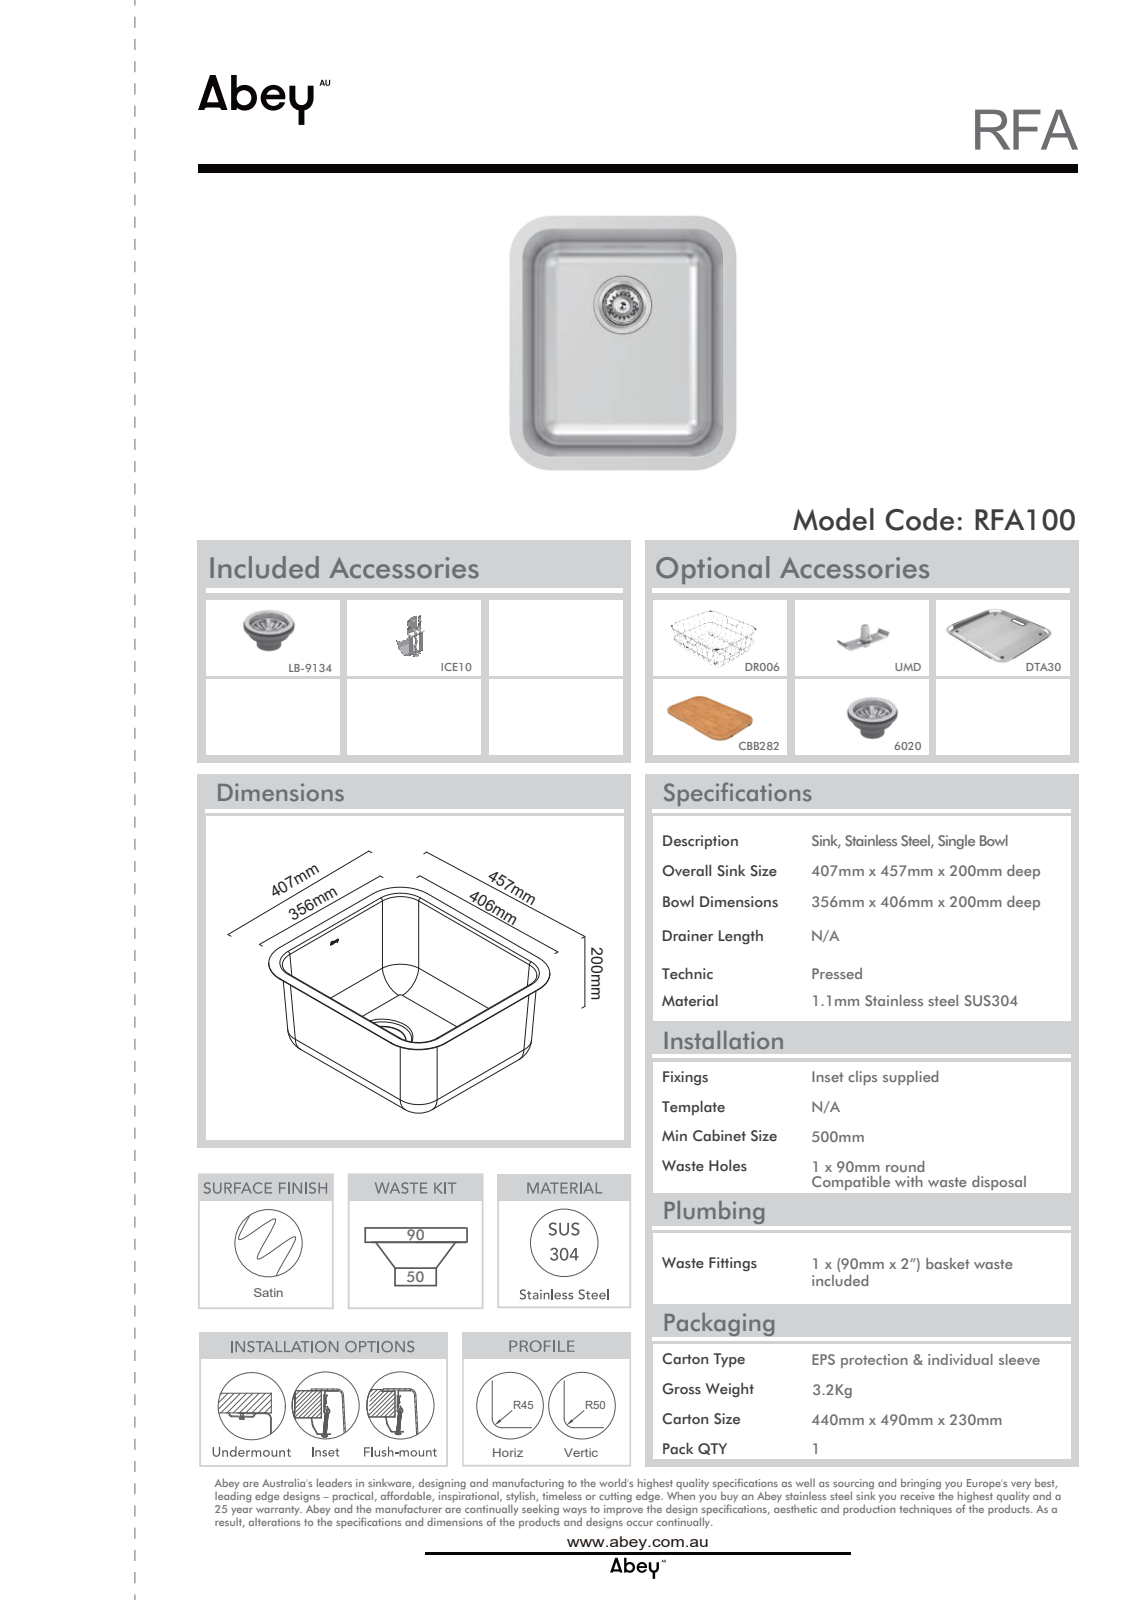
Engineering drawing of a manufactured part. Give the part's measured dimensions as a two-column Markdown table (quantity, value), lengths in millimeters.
| quantity | value |
| --- | --- |
| part name | RFA100 |
| STEP written by | SolidWorks 2022 (CONFIG_CONTROL_DESIGN) |
| units | millimeters |
| bodies | 1 solid, 73 faces (15 planar, 30 cylindrical, 28 other) |
| overall size | 457 × 407 × 210 |
| volume | 386 935 mm³ |
| surface area | 830 293 mm² |
| round holes (diameter × count) | 91.1 × 1 |
| partial cylindrical surfaces (radius × count) | 4 × 4, 5 × 4, 45 × 4, 46 × 4, 50 × 4, 51 × 4, 75 × 4 |
| main face-to-face distances | 1, 407, 457, 209, 210 |
